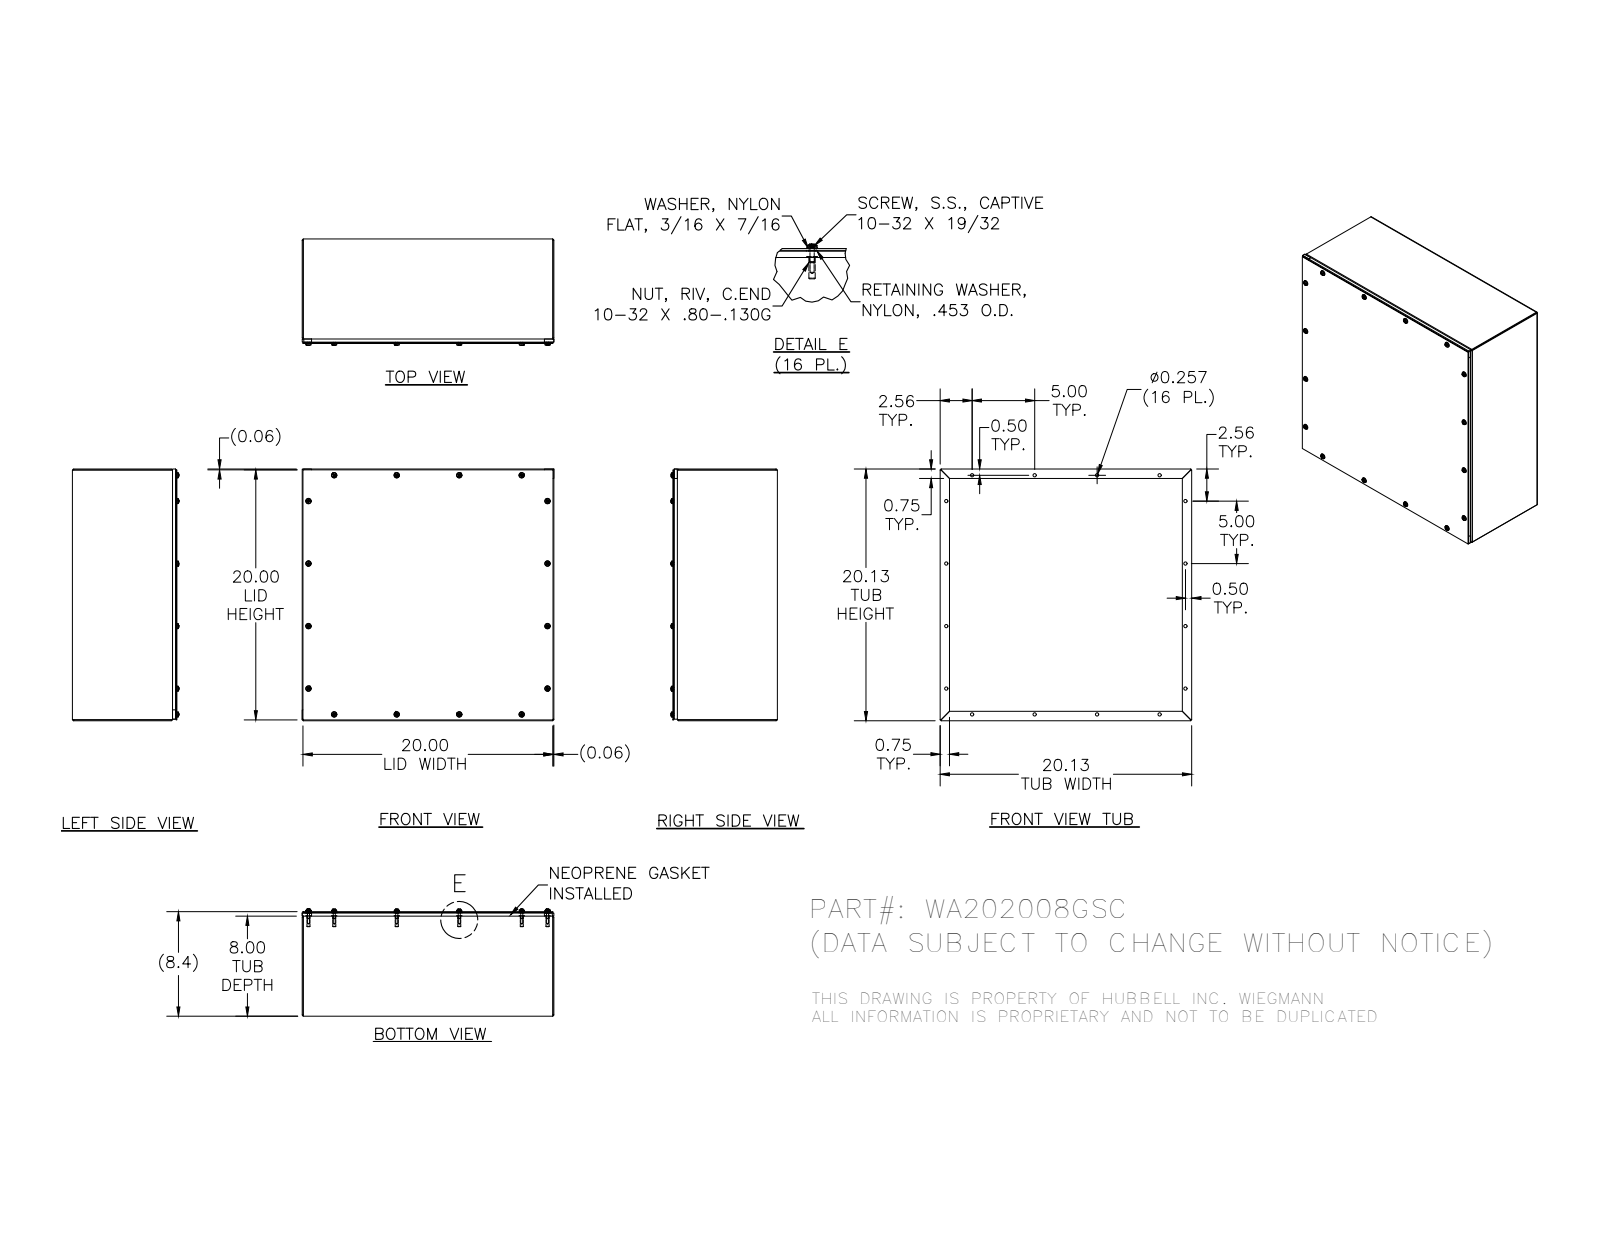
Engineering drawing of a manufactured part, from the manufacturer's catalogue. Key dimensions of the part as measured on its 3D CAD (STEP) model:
Part name (STEP PRODUCT): WA2020GSC_LP; 34984; WA202008GSCBKP; WA202008GSC (+3 more)
STEP written by: SolidWorks 2014 (AUTOMOTIVE_DESIGN)
Units: inches
Bodies: 69 solids, 1646 faces (766 planar, 432 cylindrical, 448 other)
Overall size (bounding box): 20.125 × 20.125 × 8.511
Volume: 122.1 in³ · Surface area: 3 150 in²
Round holes (diameter × count): ⌀0.188 ×16, ⌀0.257 ×16, ⌀0.278 ×16, ⌀0.281 ×16, ⌀0.156 ×15, ⌀0.196 ×15
Round bosses / shafts (diameter × count): ⌀0.453 ×16, ⌀0.437 ×16, ⌀0.167 ×16, ⌀0.406 ×15, ⌀0.248 ×15
Partial cylindrical surfaces — rounded edges, fillets, slot ends (radius × count): R0.089 ×16, R0.031 ×8, R0.105 ×8
Main face-to-face distances: 0.074, 8.282, 20.051, 8.356, 8.208, 19.977, 20.125, 20.125, 0.074, 20.051
Hole centre spacings: 5, 10, 15, 7.357, 17.187, 18.467, 19.768, 12.238
